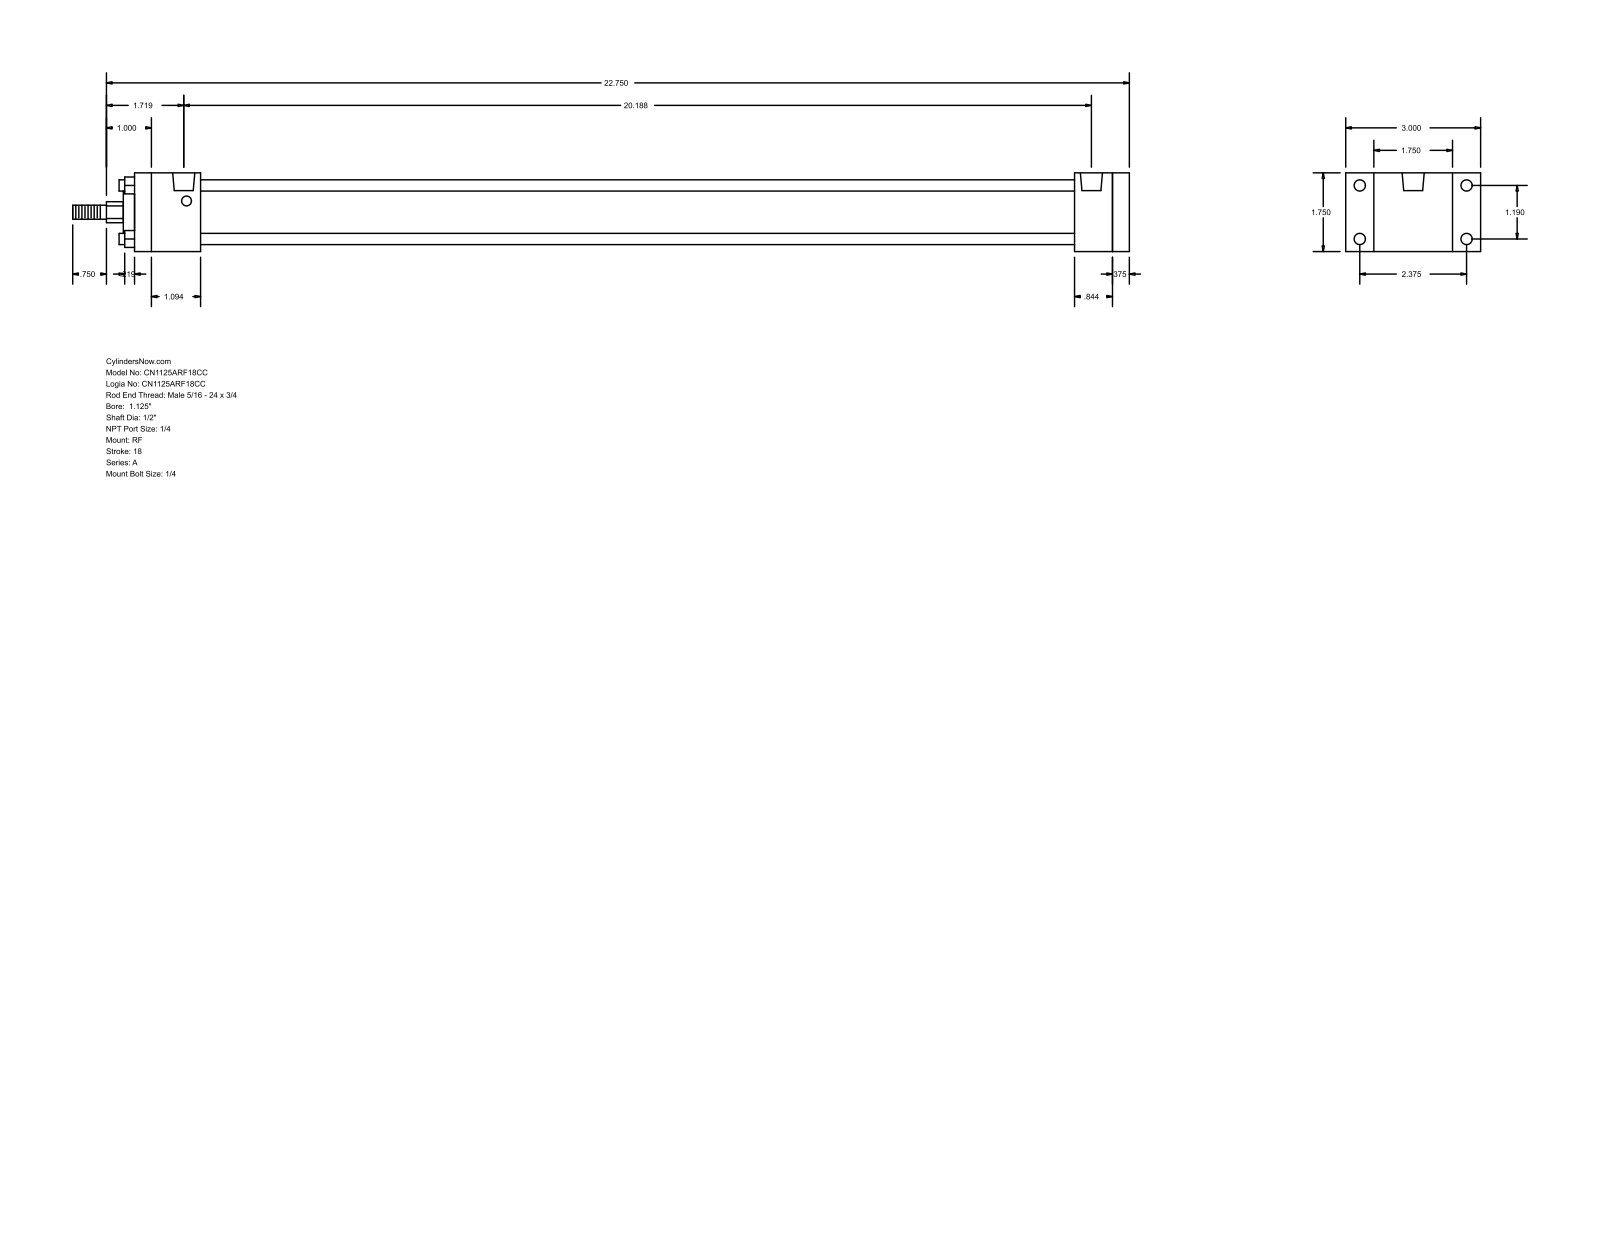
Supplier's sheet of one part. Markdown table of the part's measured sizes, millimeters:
| quantity | value |
| --- | --- |
| part name | A_RF__0112_0.5 |
| STEP written by | GSSL Pune (CONFIG_CONTROL_DESIGN) |
| units | millimeters |
| bodies | 0 solids, 92 faces (64 planar, 28 cylindrical, 0 other) |
| overall size | 596.9 × 76.2 × 44.45 |
| round holes (diameter × count) | 5.56 × 4, 6.35 × 4, 12.49 × 2 |
| round bosses / shafts (diameter × count) | 6.35 × 4, 31.88 × 1, 23.81 × 1, 12.7 × 1, 7.94 × 1 |
| partial cylindrical surfaces (radius × count) | 5.94 × 1 |
| main face-to-face distances | 44.46, 9.52, 552.45, 561.97, 37.3, 531.01, 493.71, 515.15, 524.67, 21.44 |
| hole center spacings | 30.22, 60.32, 67.47, 509.59, 1.58, 1.59, 511.17, 511.18 |
